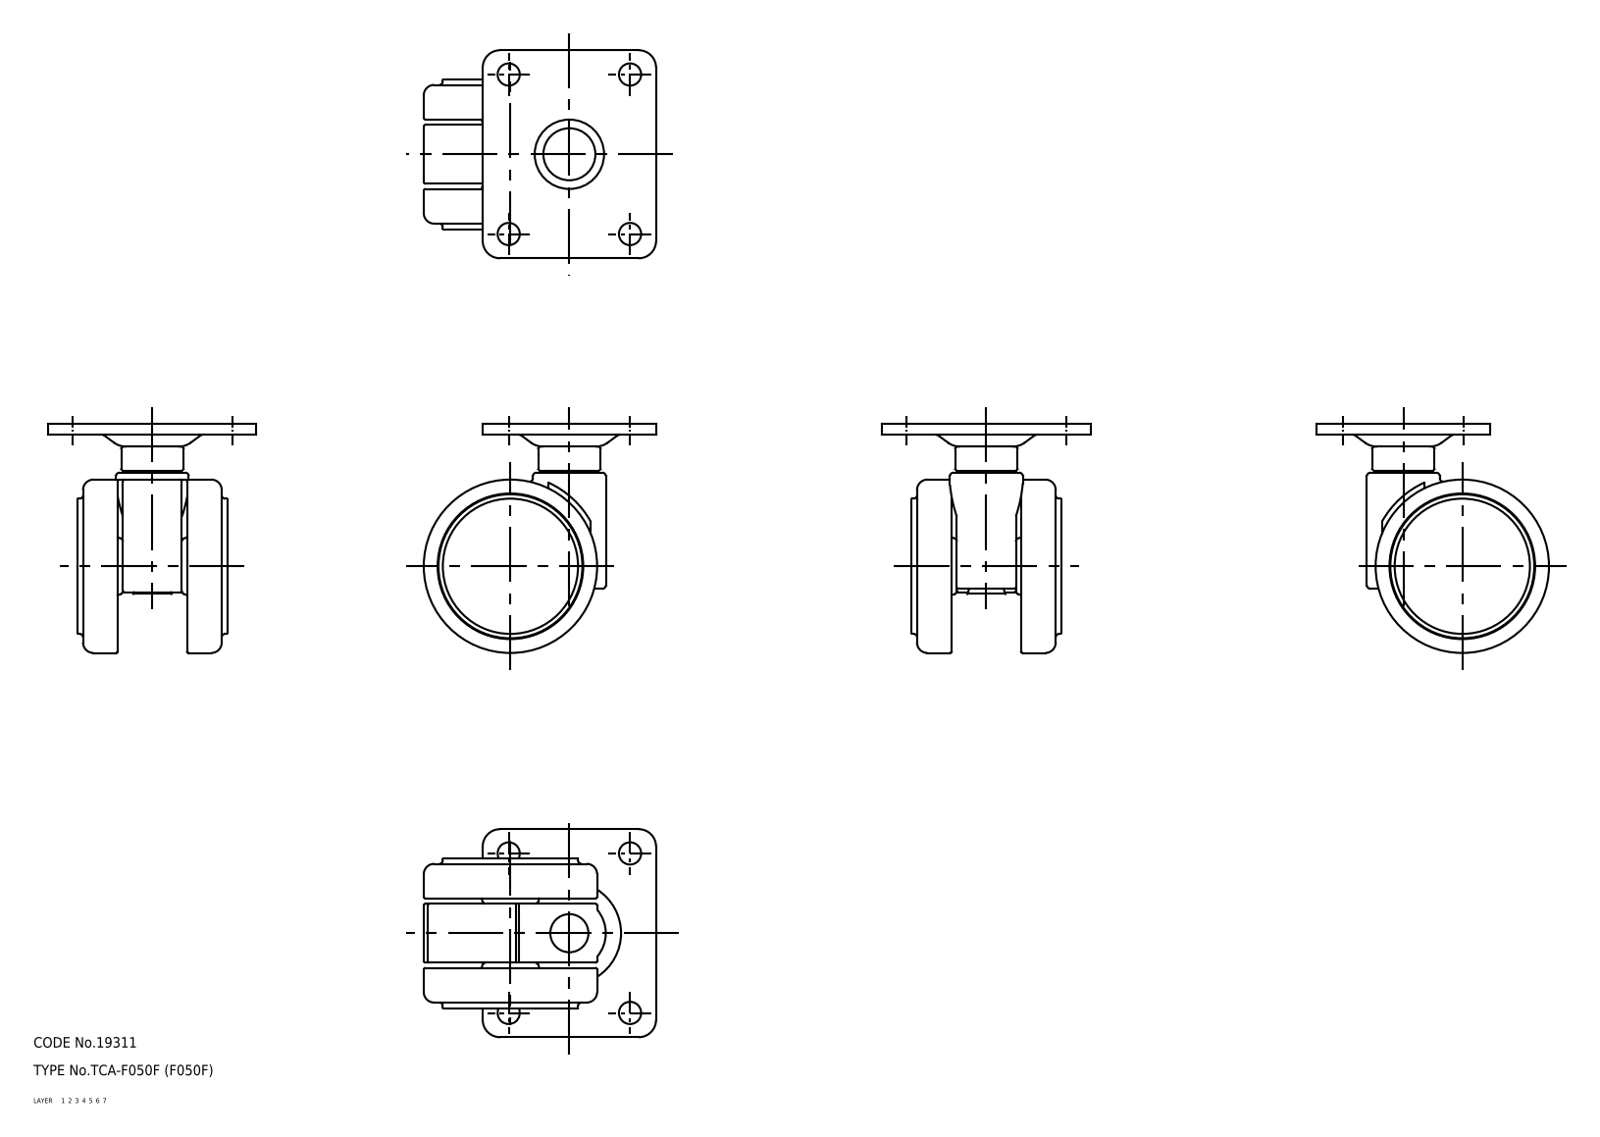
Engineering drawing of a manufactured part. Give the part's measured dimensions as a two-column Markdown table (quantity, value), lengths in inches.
| quantity | value |
| --- | --- |
| part name | 67119730; 67119743; 67119756; 67119769 (+1 more) |
| STEP written by | CADfix (AUTOMOTIVE_DESIGN) |
| units | inches |
| bodies | 5 solids, 139 faces (0 planar, 0 cylindrical, 139 other) |
| overall size | 2.638 × 2.598 × 2.362 |
| volume | 4.302 in³ |
| surface area | 43.98 in² |
